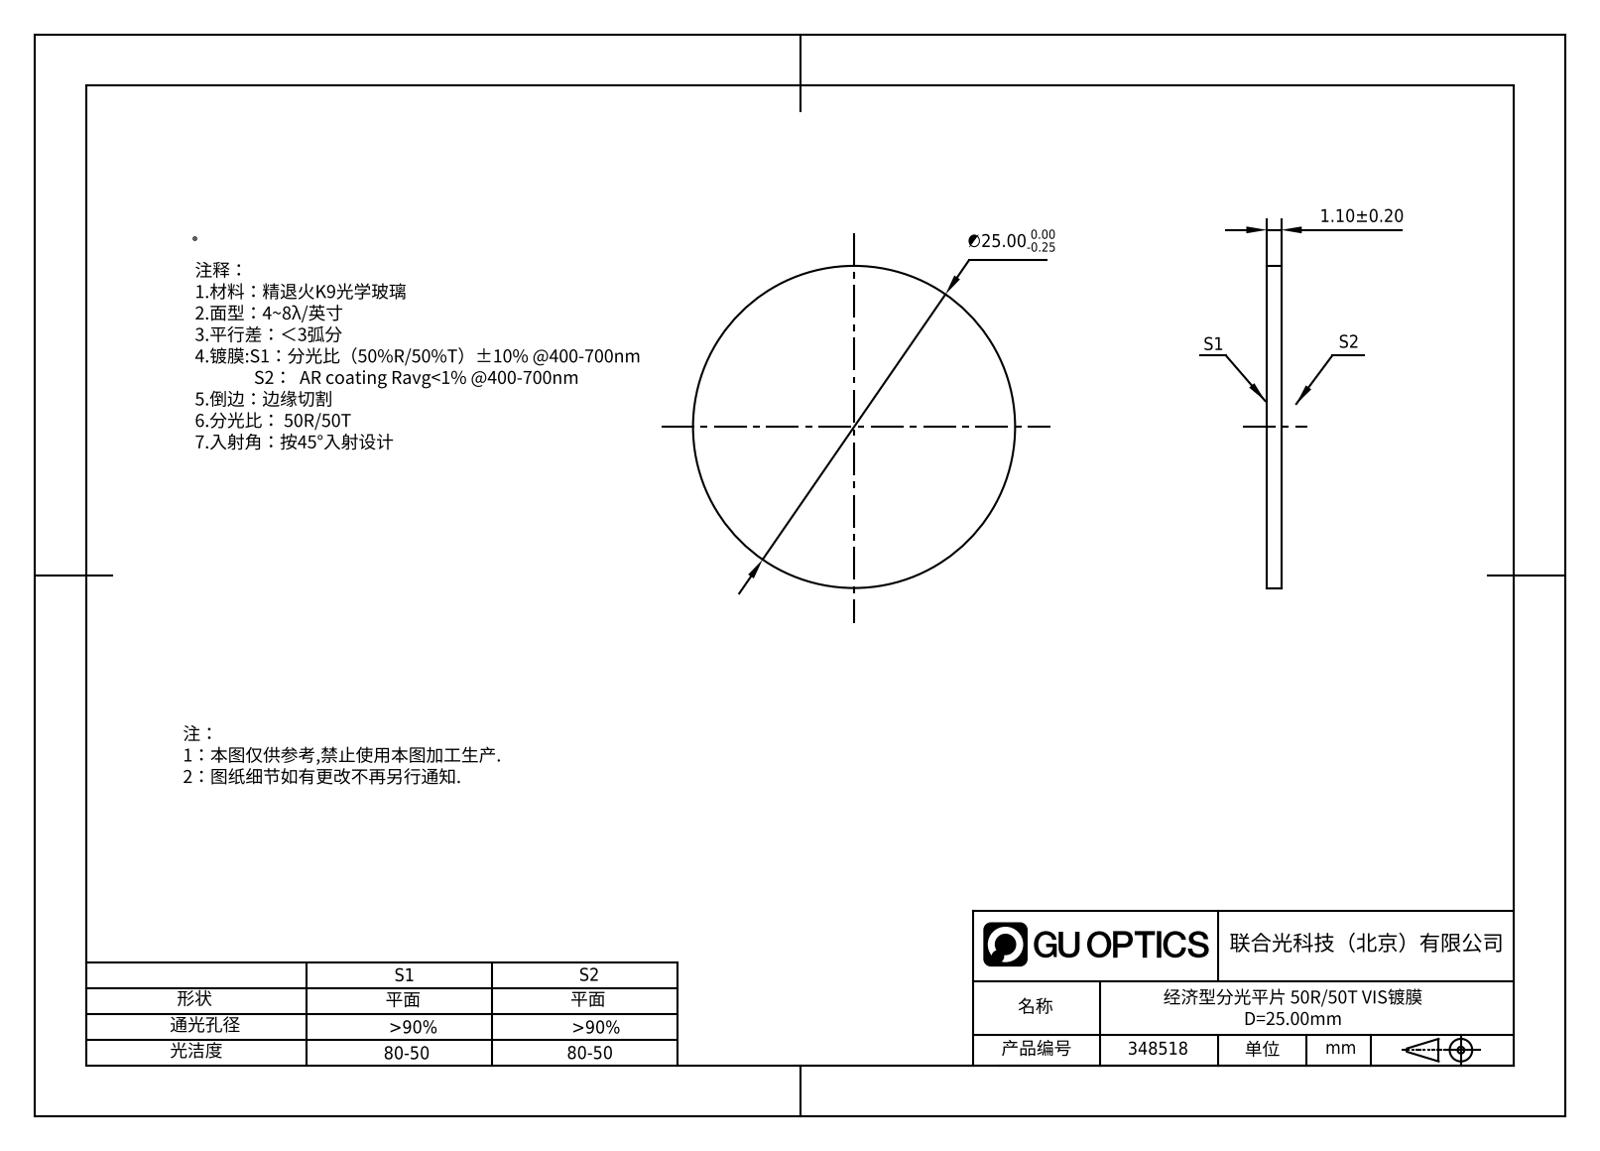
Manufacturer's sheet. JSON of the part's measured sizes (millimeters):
{"part_name": "348504", "step_written_by": "SolidWorks 2016 (CONFIG_CONTROL_DESIGN)", "units": "millimeters", "bodies": {"solids": 1, "faces": 6, "planar": 6, "cylindrical": 0, "other": 0}, "overall_size": [30, 20, 1.1], "volume_mm3": 660, "surface_area_mm2": 1310, "face_to_face_distances": [1.1, 20, 30]}
